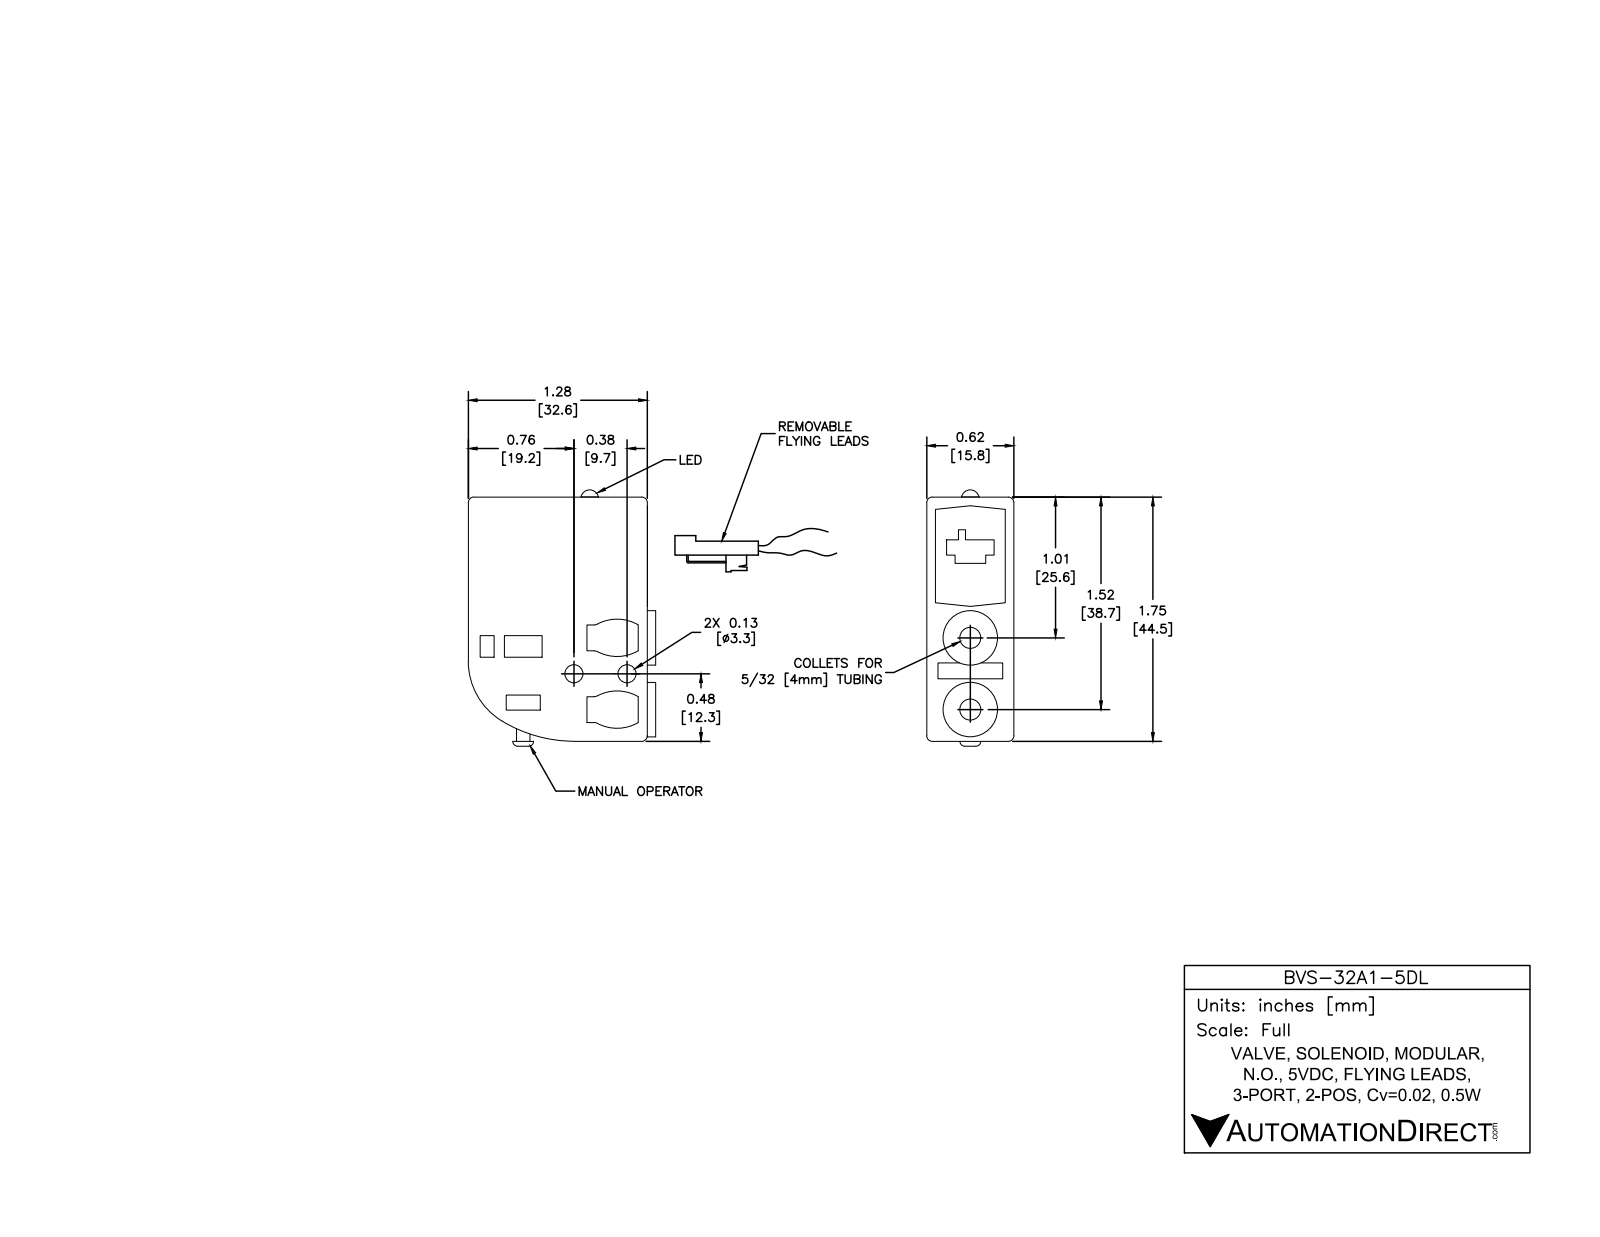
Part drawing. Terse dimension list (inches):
name: BVS-32A1-5DL
written by: SolidWorks 2016 (AUTOMOTIVE_DESIGN)
unit: in
bodies: 1 solid, 149 faces (83 planar, 54 cylindrical, 12 other)
size: 1.84 × 1.788 × 0.62
volume: 1.259 in³; area: 10.37 in²
holes: 2× ⌀0.13, 2× ⌀0.15, 2× ⌀0.25, 1× ⌀0.05
bosses: 6× ⌀0.06, 2× ⌀0.39, 1× ⌀0.1
rounds: 4× R0.05, 4× R0.3, 3× R0.04, 1× R0.5, 1× R1
face distances: 0.62, 0.1, 1.29, 0.52, 1.291, 1.75, 1, 0.15, 0.06, 1.35
hole spacings: 0.06, 0.38, 0.45, 0.51
